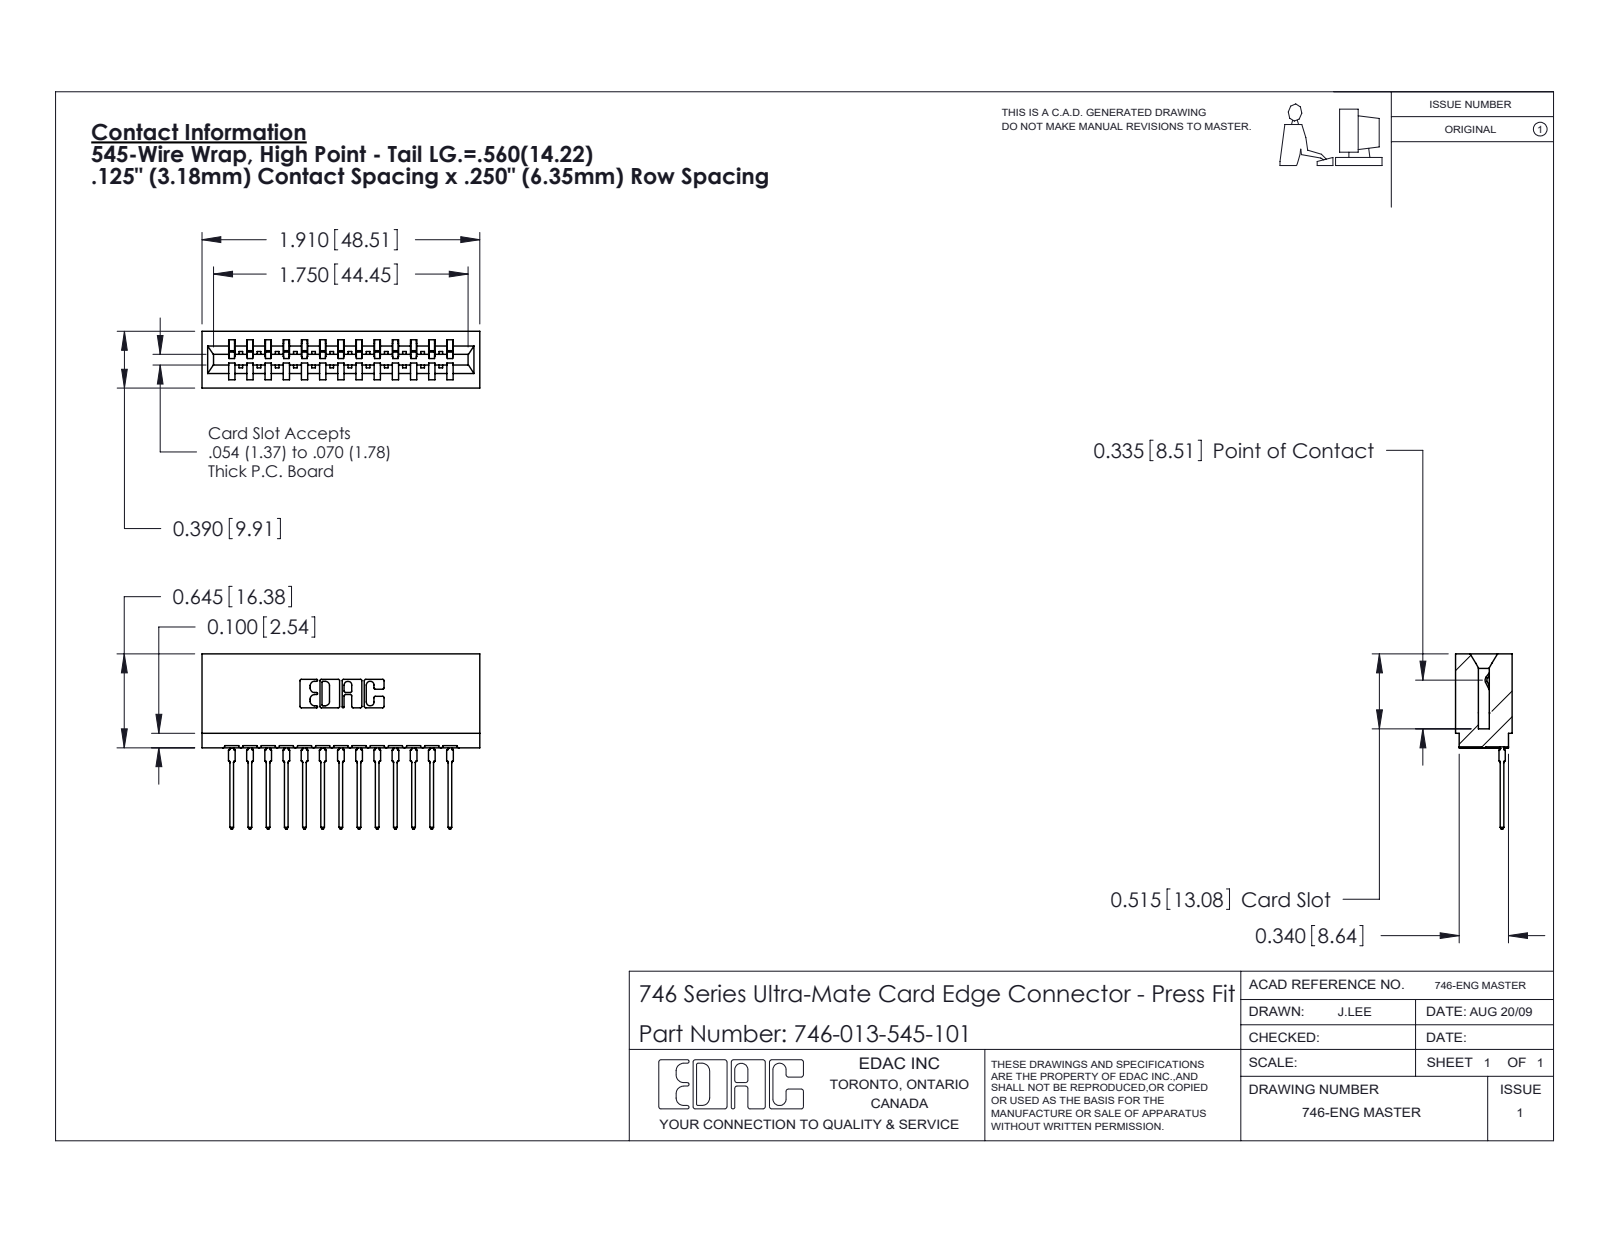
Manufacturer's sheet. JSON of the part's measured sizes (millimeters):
{"part_name": "746-292-001_545; 746-013-545-101; 746 Part_.515 Slot Depth - 01", "step_written_by": "SolidWorks 2020 (CONFIG_CONTROL_DESIGN)", "units": "millimeters", "bodies": {"solids": 14, "faces": 1501, "planar": 874, "cylindrical": 289, "other": 338}, "overall_size": [48.5, 30.6, 9.9], "volume_mm3": 5310, "surface_area_mm2": 7555, "partial_cylinders_radius": [[0.5, 26], [0.3, 22], [0.4, 14], [0.2, 6], [0.8, 6], [0.1, 4], [0.3, 4], [0.7, 3]], "face_to_face_distances": [6.4, 8.5, 1.4, 12.7, 9.9, 3.2, 3.2, 1.1, 5.3, 2.1]}
